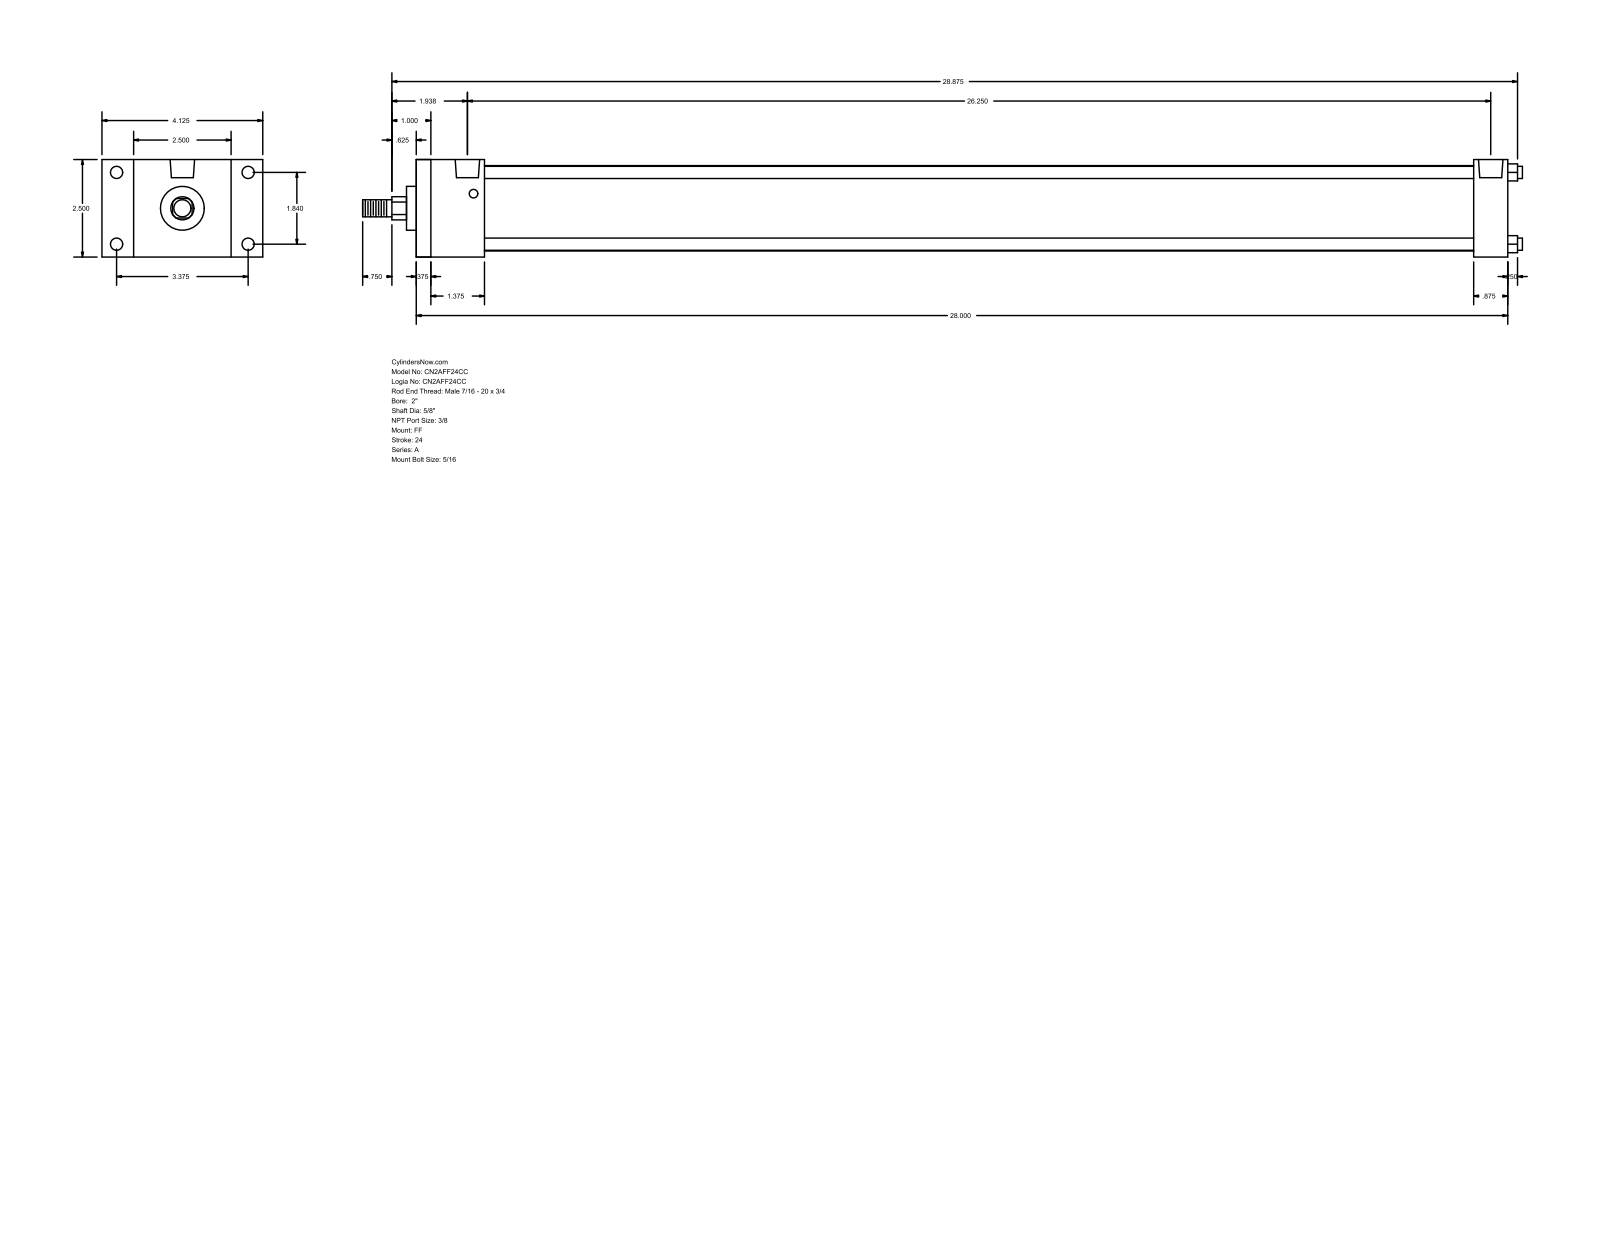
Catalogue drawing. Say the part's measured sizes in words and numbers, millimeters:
The part is named "A_FF__0200_0.625". Its 3-D file was written by "GSSL Pune (CONFIG_CONTROL_DESIGN)". It is 0 solids with 92 faces: 64 planar, 28 cylindrical and 0 other. Overall it measures 755.65 by 104.78 by 63.5 millimeters. Round holes: 4 of diameter 5.56, 4 of diameter 7.94, 2 of diameter 15.93. Round bosses or shafts: 4 of diameter 7.94, 1 of diameter 55.63, 1 of diameter 28.57, 1 of diameter 15.88, 1 of diameter 11.11. Partial cylindrical surfaces (rounded edges, fillets, slot ends): 1 of radius 7.54. The main face-to-face distances are 63.5, 711.2, 9.52, 701.68, 34.93, 44.45, 688.97, 679.45, 644.52, 666.75. The hole center spacings are 46.74, 85.72, 97.63, 658.8, 3.97, 3.98, 662.77, 662.78.
